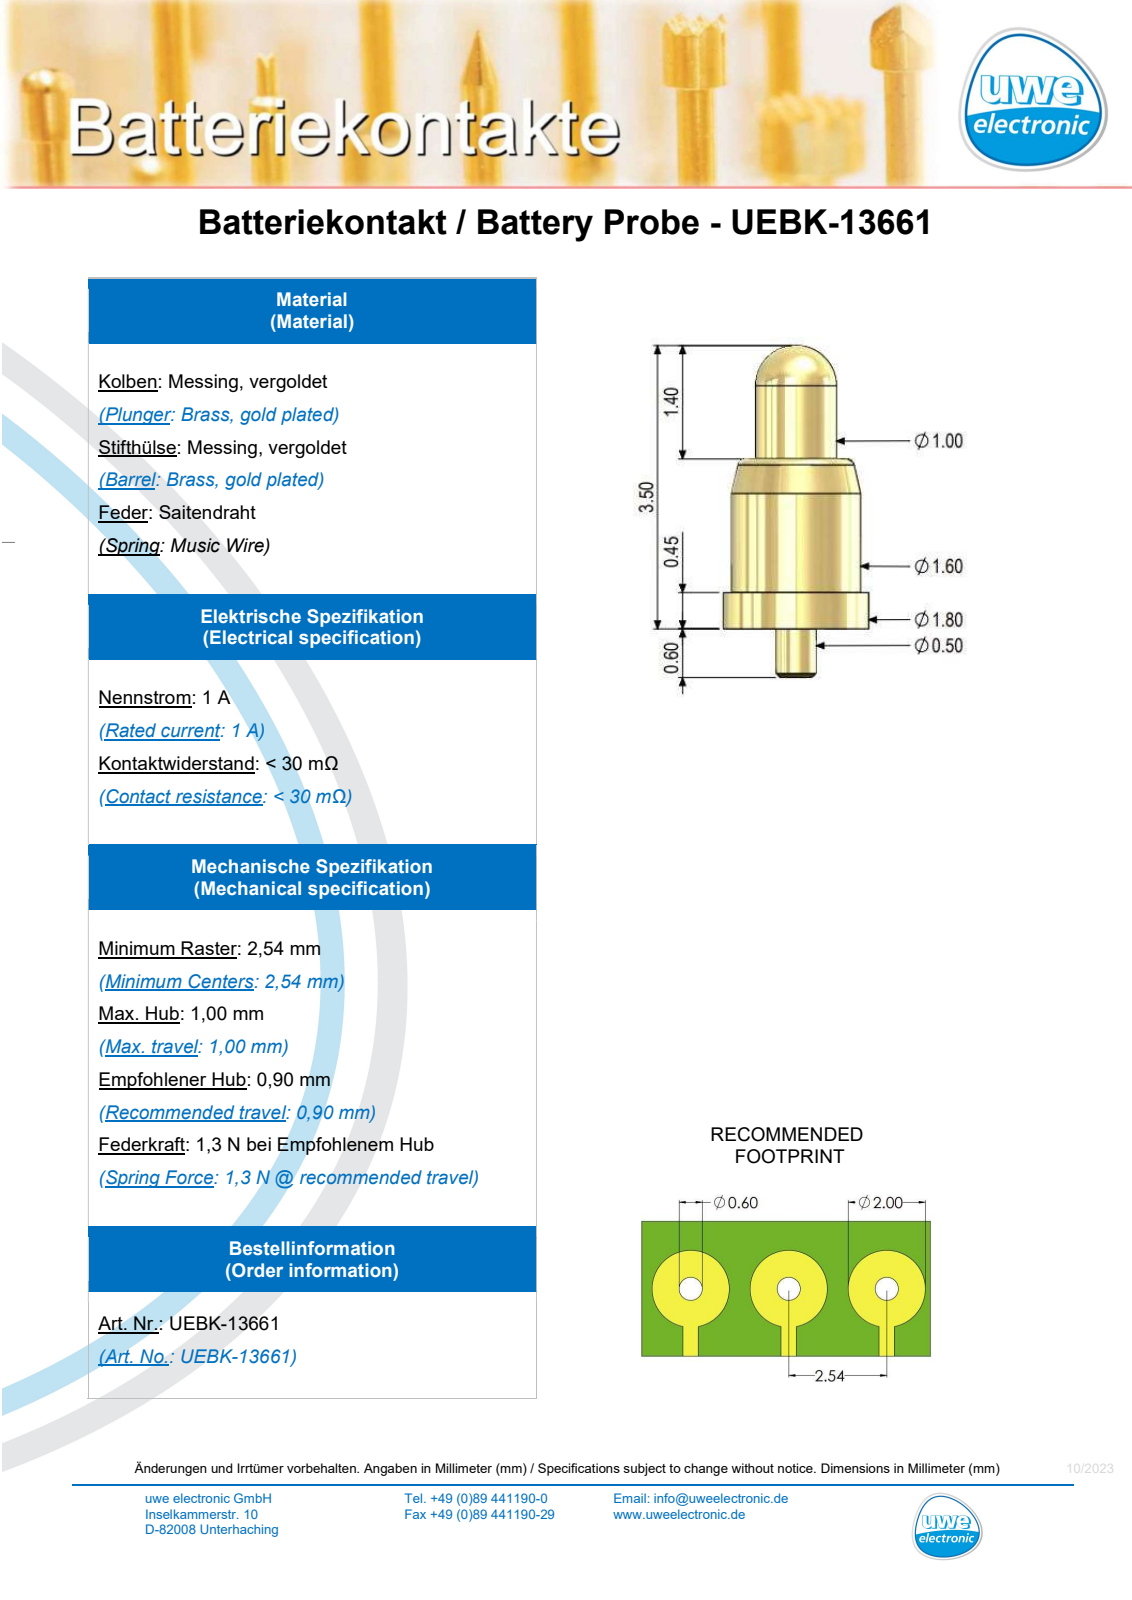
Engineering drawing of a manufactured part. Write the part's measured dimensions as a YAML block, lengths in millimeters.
part_name: "UEBK-13661_step"
step_written_by: "SolidWorks 2022 (AUTOMOTIVE_DESIGN)"
units: millimeters
bodies: {solids: 1, faces: 19, planar: 4, cylindrical: 8, other: 7}
overall_size: [4.1, 1.8, 1.8]
volume: 5
surface_area: 20
round_bosses_or_shafts:
  - {diameter: 1.8, count: 1}
  - {diameter: 1.6, count: 1}
  - {diameter: 1, count: 1}
  - {diameter: 0.5, count: 1}
face_to_face_distances: [0.45, 2.1, 1.65, 0.6, 1.05, 2.7]
